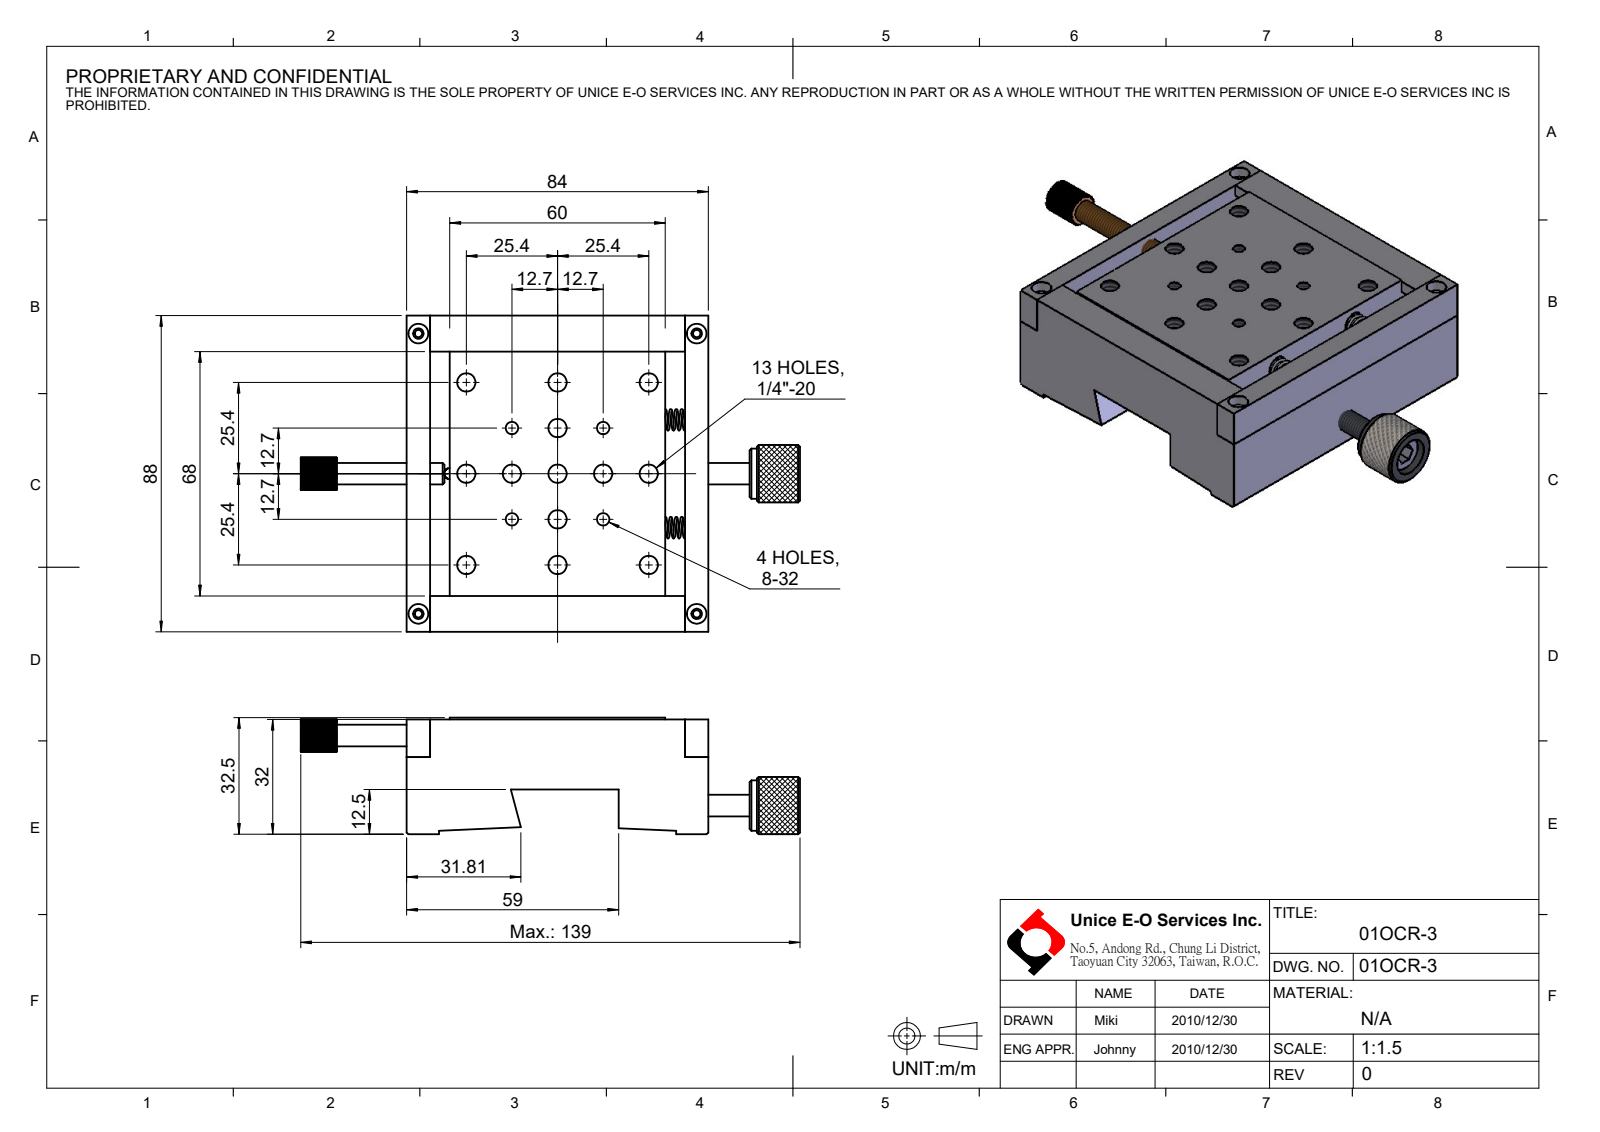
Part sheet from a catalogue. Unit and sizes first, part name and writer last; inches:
Units: inches
Overall size (bounding box): 5.472 × 3.465 × 1.28
Round holes (diameter × count): ⌀0.201 ×13, ⌀0.081 ×4, ⌀0.114 ×4, ⌀0.136 ×4, ⌀0.217 ×4, ⌀0.197 ×2, ⌀0.248 ×2, ⌀0.098 ×1, ⌀0.413 ×1
Round bosses / shafts (diameter × count): ⌀0.236 ×2, ⌀0.63 ×1, ⌀0.551 ×1, ⌀0.394 ×1, ⌀0.157 ×1
Partial cylindrical surfaces — rounded edges, fillets, slot ends (radius × count): R0.177 ×1
Main face-to-face distances: 0.394, 0.02, 0.413, 0.374, 0.256, 3.307, 0.787, 0.197, 0.768, 0.354
Hole centre spacings: 1.118, 0.707, 1, 0.5, 1.581, 1.414, 1.803, 2.236
Volume: 11.72 in³ · Surface area: 84.53 in²
Bodies: 11 solids, 380 faces (204 planar, 147 cylindrical, 29 other)
Part name (STEP PRODUCT): 01OCR-3
STEP written by: SolidWorks 2016 (CONFIG_CONTROL_DESIGN)
